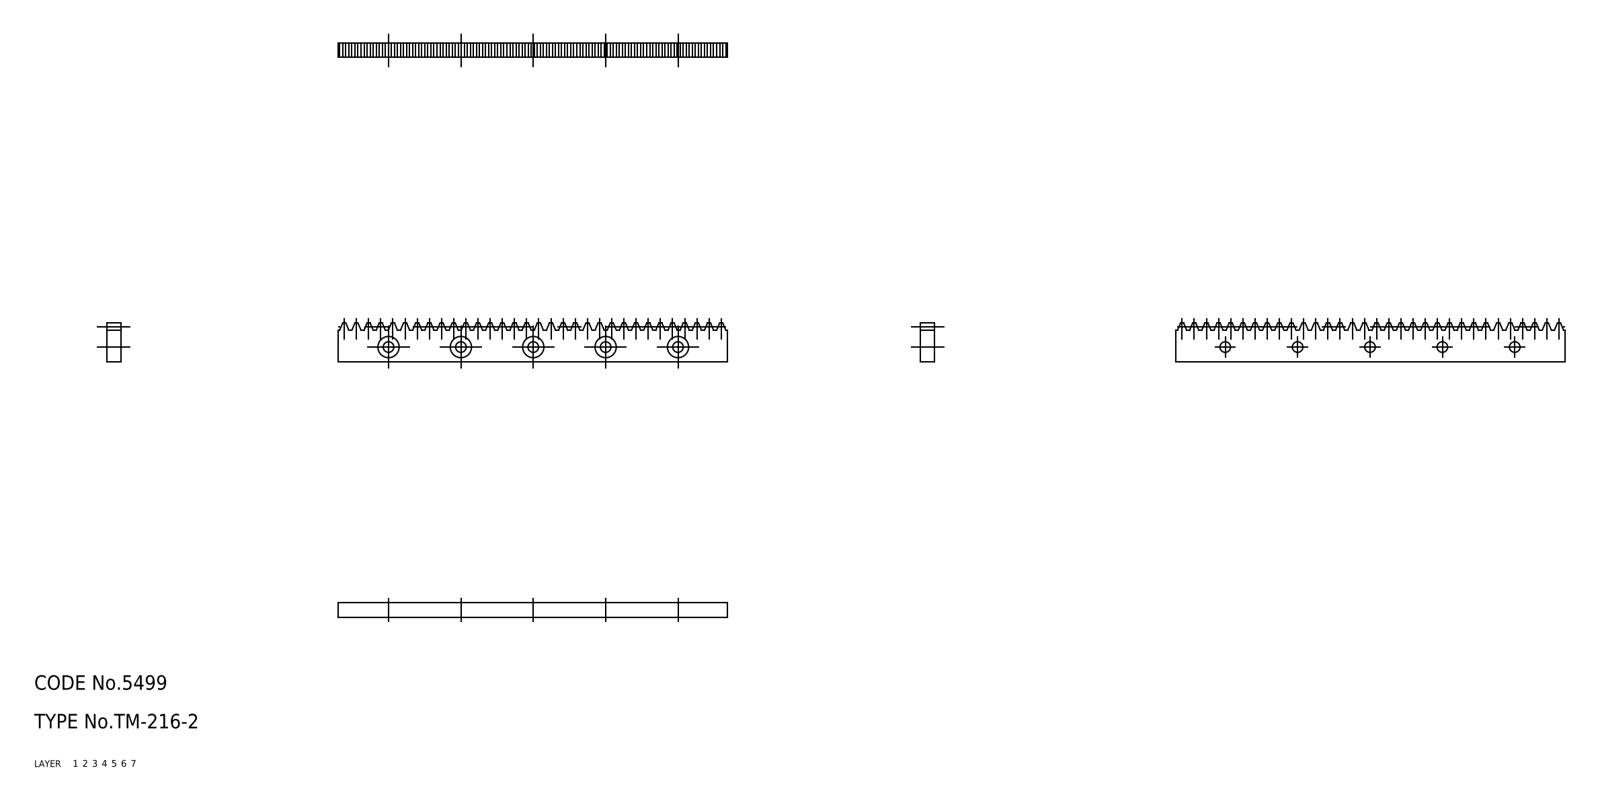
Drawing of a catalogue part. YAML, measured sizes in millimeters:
part_name: "rack"
step_written_by: "CADfix (AUTOMOTIVE_DESIGN)"
units: millimeters
bodies: {solids: 1, faces: 154, planar: 0, cylindrical: 0, other: 154}
overall_size: [80.64, 8, 3]
volume: 1669
surface_area: 1935
